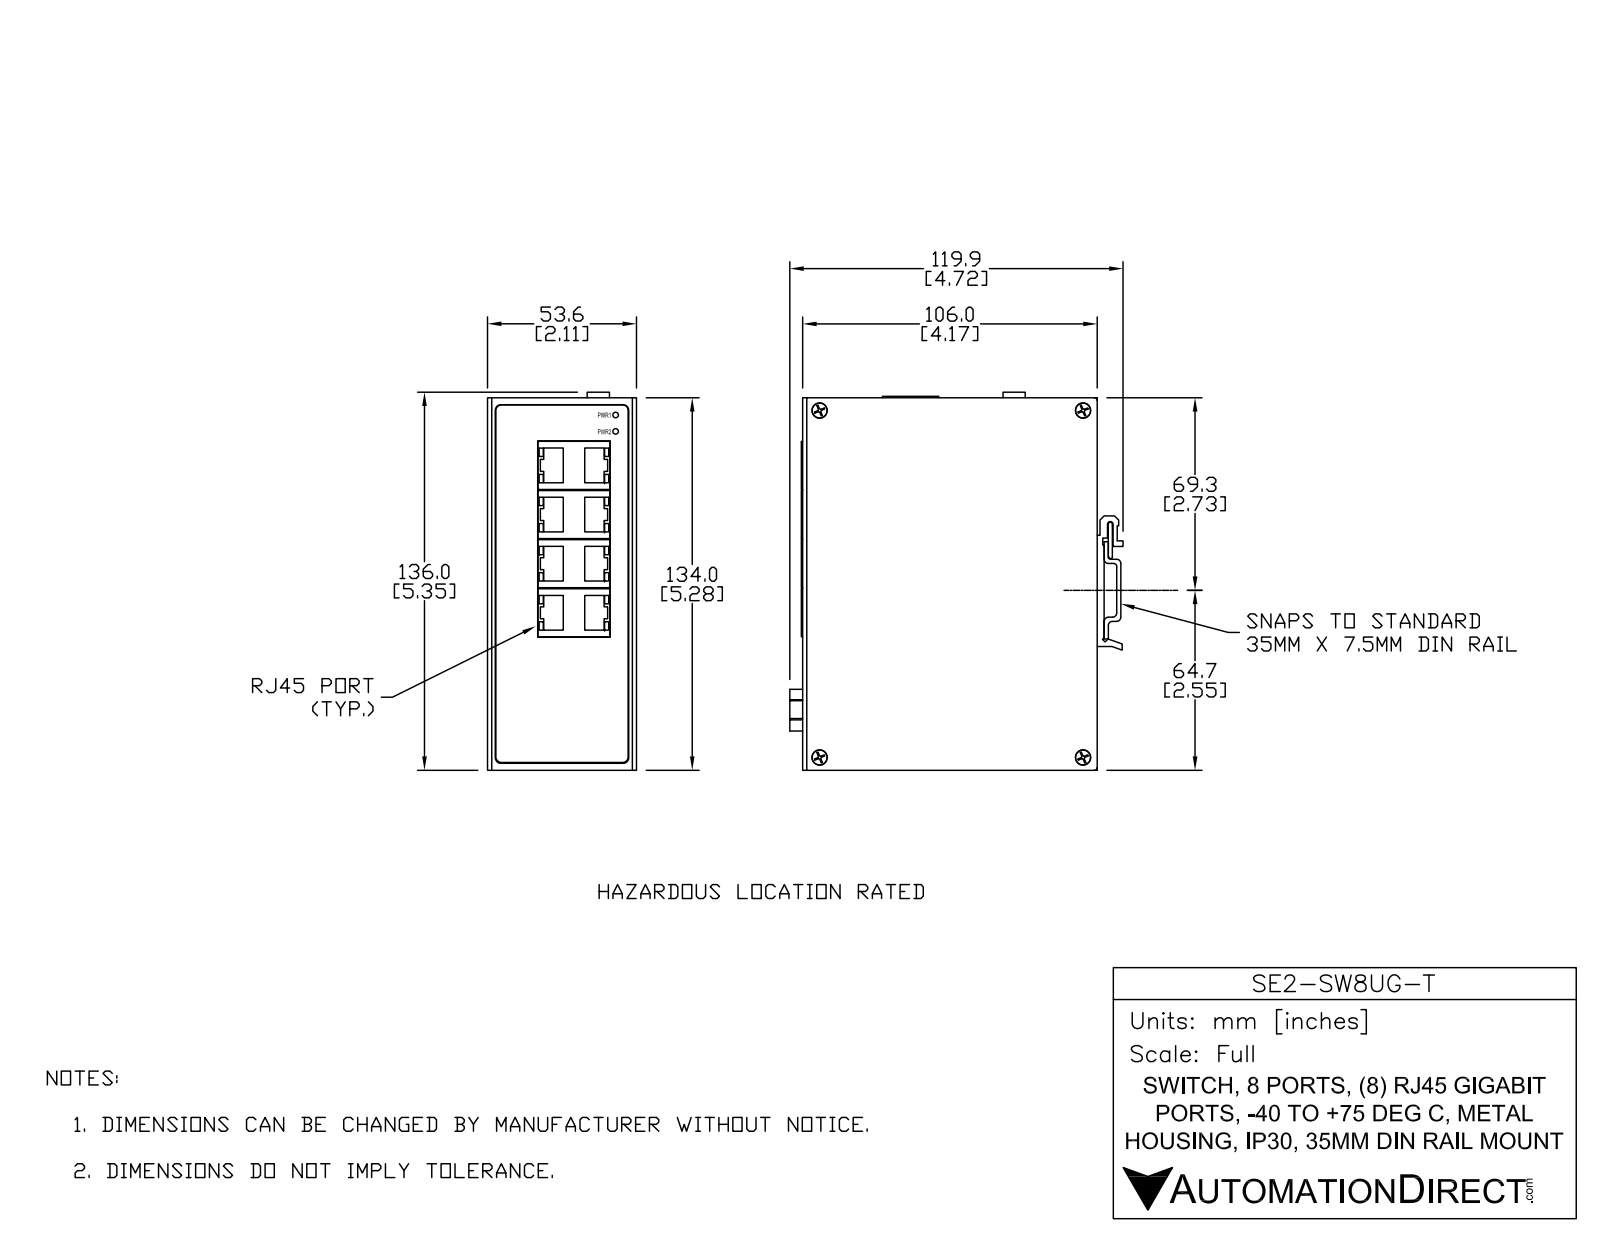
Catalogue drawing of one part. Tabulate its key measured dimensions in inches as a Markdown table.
| quantity | value |
| --- | --- |
| part name | SE2-SW8UG-T |
| STEP written by | SolidWorks 2017 (AUTOMOTIVE_DESIGN) |
| units | inches |
| bodies | 24 solids, 1758 faces (1181 planar, 470 cylindrical, 107 other) |
| overall size | 5.732 × 4.569 × 2.11 |
| volume | 7.54 in³ |
| surface area | 266.9 in² |
| round holes (diameter × count) | 0.098 × 9, 0.11 × 7, 0.118 × 6, 0.051 × 4, 0.15 × 4, 0.122 × 2, 0.138 × 2, 0.157 × 2, 0.197 × 1 |
| round bosses / shafts (diameter × count) | 0.248 × 9, 0.138 × 7, 0.197 × 4, 0.142 × 4, 0.118 × 4, 0.051 × 4, 0.024 × 4, 0.315 × 1 |
| partial cylindrical surfaces (radius × count) | 0.025 × 180, 0.079 × 8, 0.118 × 8, 0.041 × 6, 0.039 × 5, 0.004 × 4, 0.012 × 4, 0.043 × 4 |
| main face-to-face distances | 0.039, 0.04, 2.071, 2.031, 0.079, 2.031, 0.02, 2.11, 2.07, 5.236 |
| hole center spacings | 0.544, 0.2, 5.938, 0.203, 0.4, 0.4, 0.582, 1.024 |
